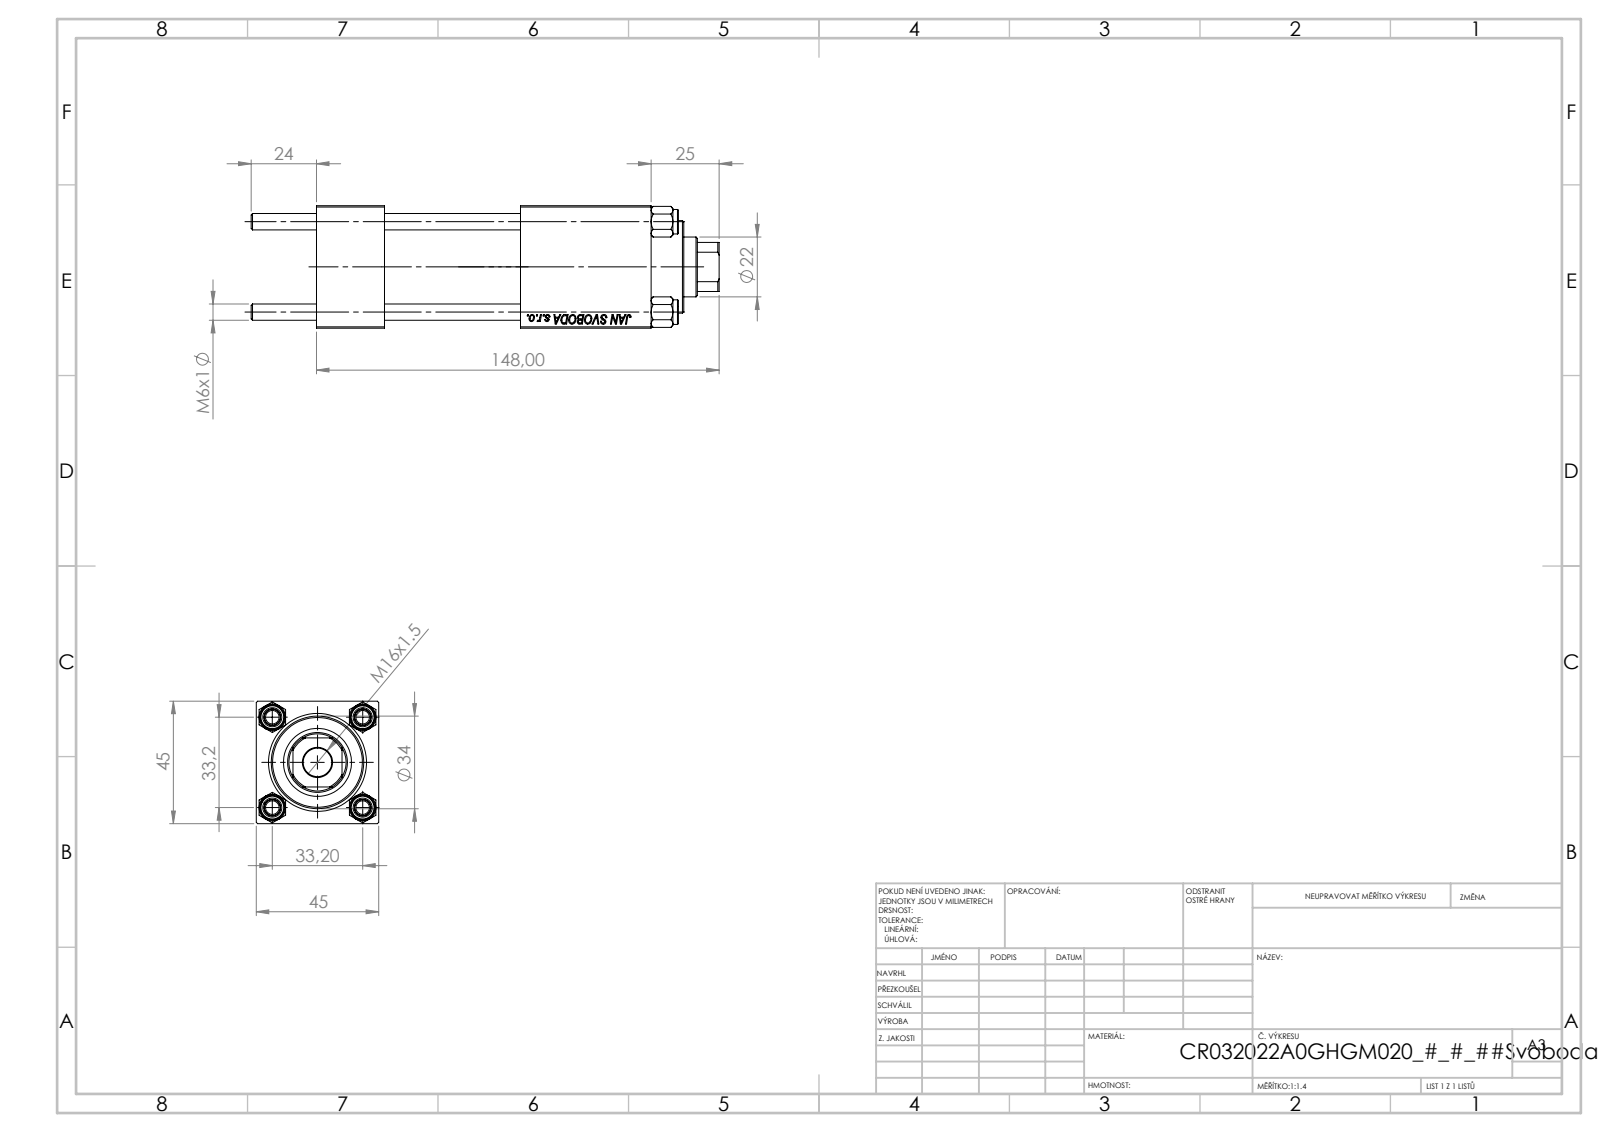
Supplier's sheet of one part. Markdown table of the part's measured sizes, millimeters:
| quantity | value |
| --- | --- |
| part name | CR025_012_A_0_G_A_G_M_020_+#_##_TYCINKA; V215CR_VCP; NUT_M5; V215_VC_A (+1 more) |
| STEP written by | SolidWorks 2019 (CONFIG_CONTROL_DESIGN) |
| units | millimeters |
| bodies | 11 solids, 1133 faces (519 planar, 78 cylindrical, 536 other) |
| overall size | 172 × 45 × 45 |
| volume | 214 274 mm³ |
| surface area | 77 041 mm² |
| round holes (diameter × count) | 6 × 4, 7 × 2, 13.16 × 2, 20 × 2, 10.5 × 1, 22 × 1, 24 × 1, 25 × 1, 32 × 1, 33 × 1 |
| round bosses / shafts (diameter × count) | 9 × 4, 38 × 1, 34 × 1 |
| partial cylindrical surfaces (radius × count) | 10.5 × 1 |
| main face-to-face distances | 45, 25, 123, 50, 75, 98, 48, 94.3, 69.3, 19.3 |
| hole center spacings | 23.48, 33.2, 46.95, 75.5 |
